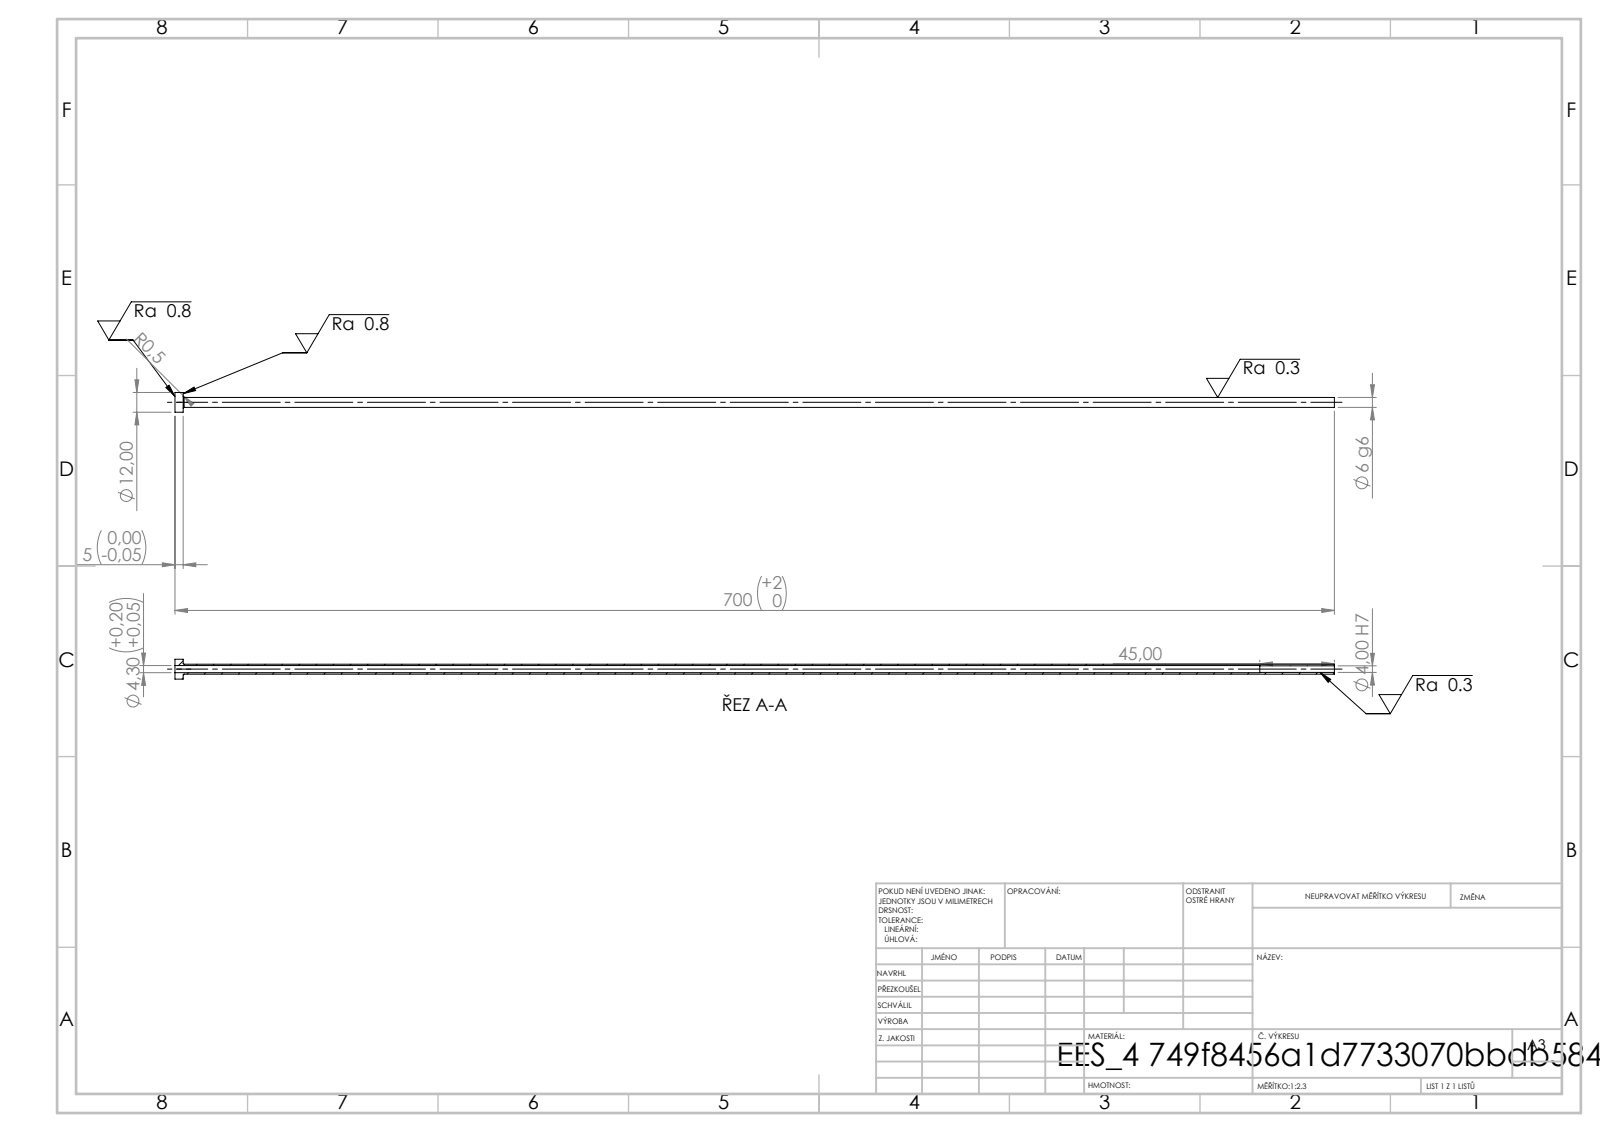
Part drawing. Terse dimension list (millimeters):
written by: SolidWorks 2019 (CONFIG_CONTROL_DESIGN)
unit: mm
bodies: 1 solid, 14 faces (4 planar, 8 cylindrical, 2 other)
size: 700 × 12 × 12
volume: 10 140 mm³; area: 22 900 mm²
holes: 1× ⌀4, 1× ⌀4.3
bosses: 1× ⌀12, 1× ⌀6
face distances: 5, 700, 695, 655, 650, 45
